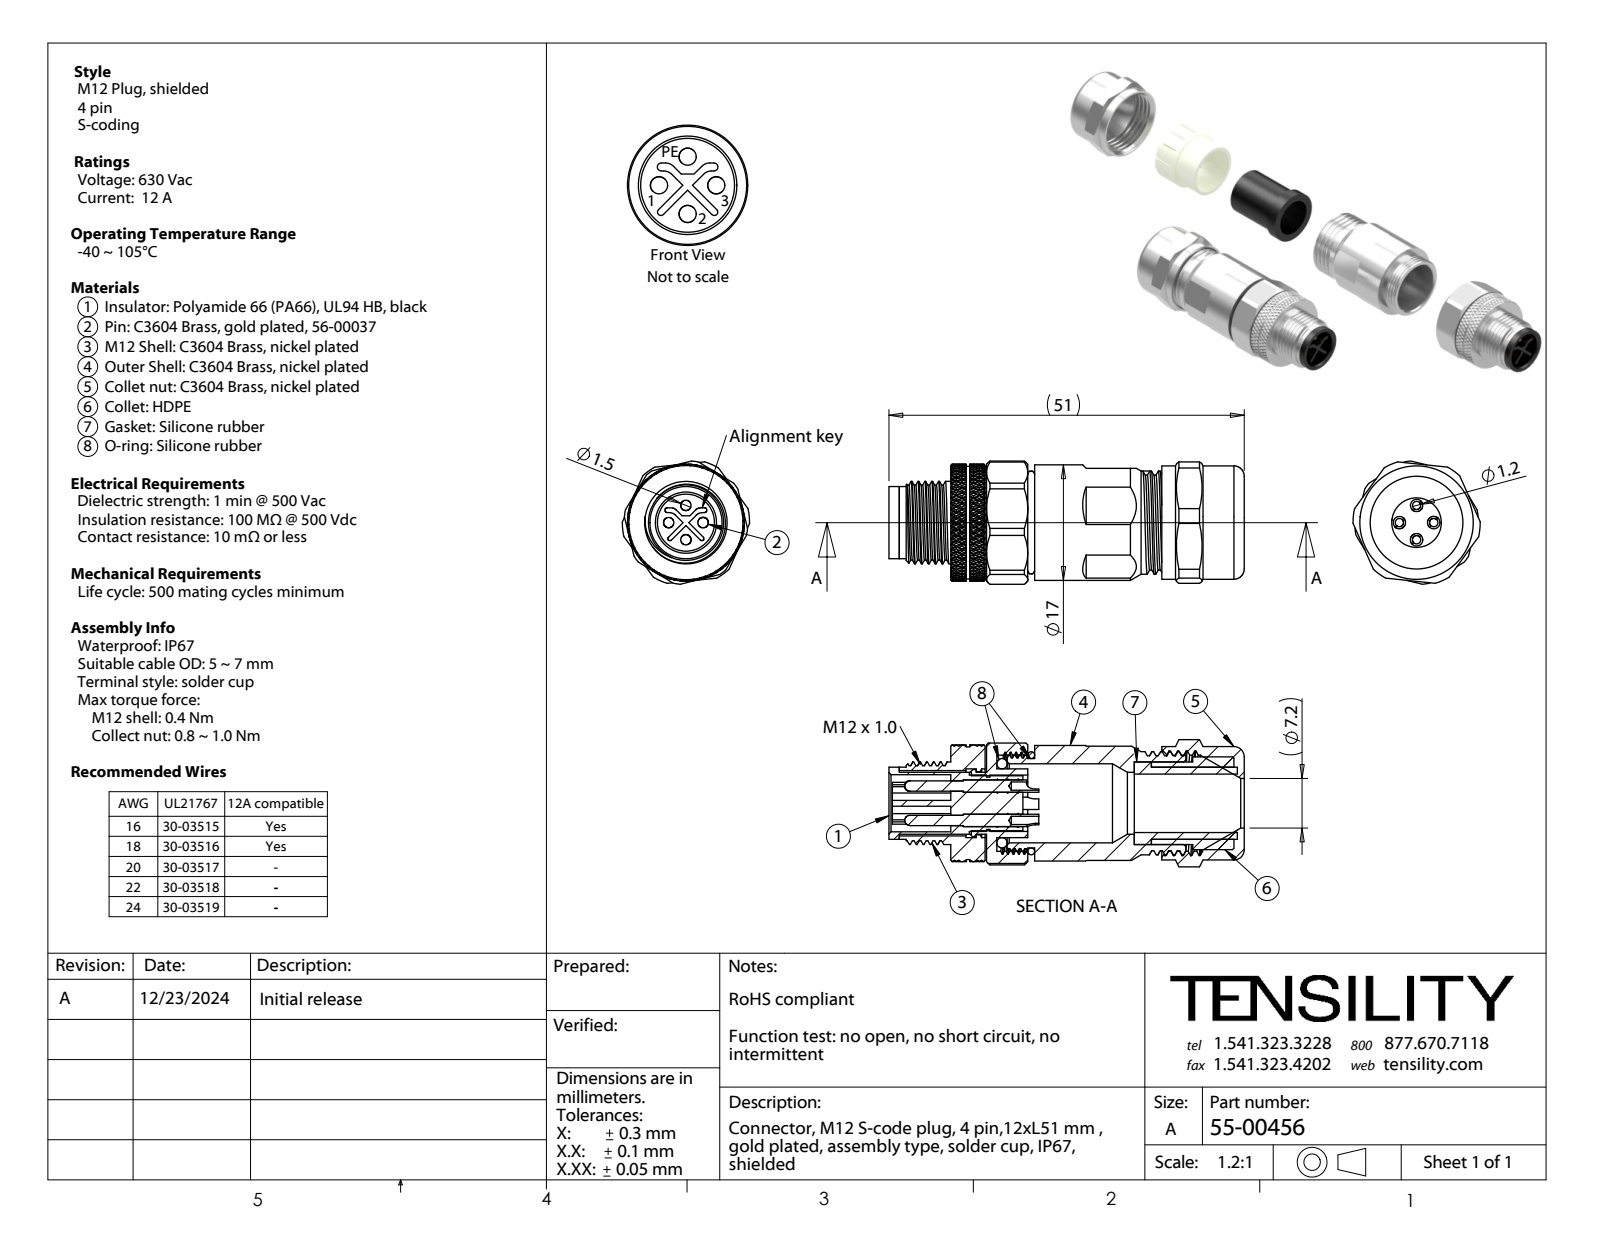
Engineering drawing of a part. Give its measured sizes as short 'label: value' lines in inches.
name: 55-00456-04; 55-00456-03; 55-00456-09; 55-00456-08 (+8 more)
written by: SolidWorks 2021 (CONFIG_CONTROL_DESIGN)
unit: in
bodies: 13 solids, 525 faces (174 planar, 209 cylindrical, 142 other)
size: 2.035 × 0.728 × 0.706
volume: 0.432 in³; area: 17.54 in²
holes: 4× ⌀0.047, 4× ⌀0.059, 1× ⌀0.283, 1× ⌀0.299, 1× ⌀0.323, 1× ⌀0.327, 1× ⌀0.335, 1× ⌀0.362, 1× ⌀0.374, 1× ⌀0.394, 1× ⌀0.453, 1× ⌀0.551
bosses: 4× ⌀0.071, 1× ⌀0.669, 1× ⌀0.661, 1× ⌀0.65, 1× ⌀0.646, 1× ⌀0.591, 1× ⌀0.531, 1× ⌀0.512
rounds: 2× R0.012, 2× R0.014, 2× R0.039, 2× R0.05, 2× R0.067, 1× R0.354, 1× R0.364
face distances: 0.669, 0.059, 0.197, 0.236, 0.295, 0.039, 0.205, 1.201, 1.681, 0.571
hole spacings: 0.098, 0.139, 0.197
